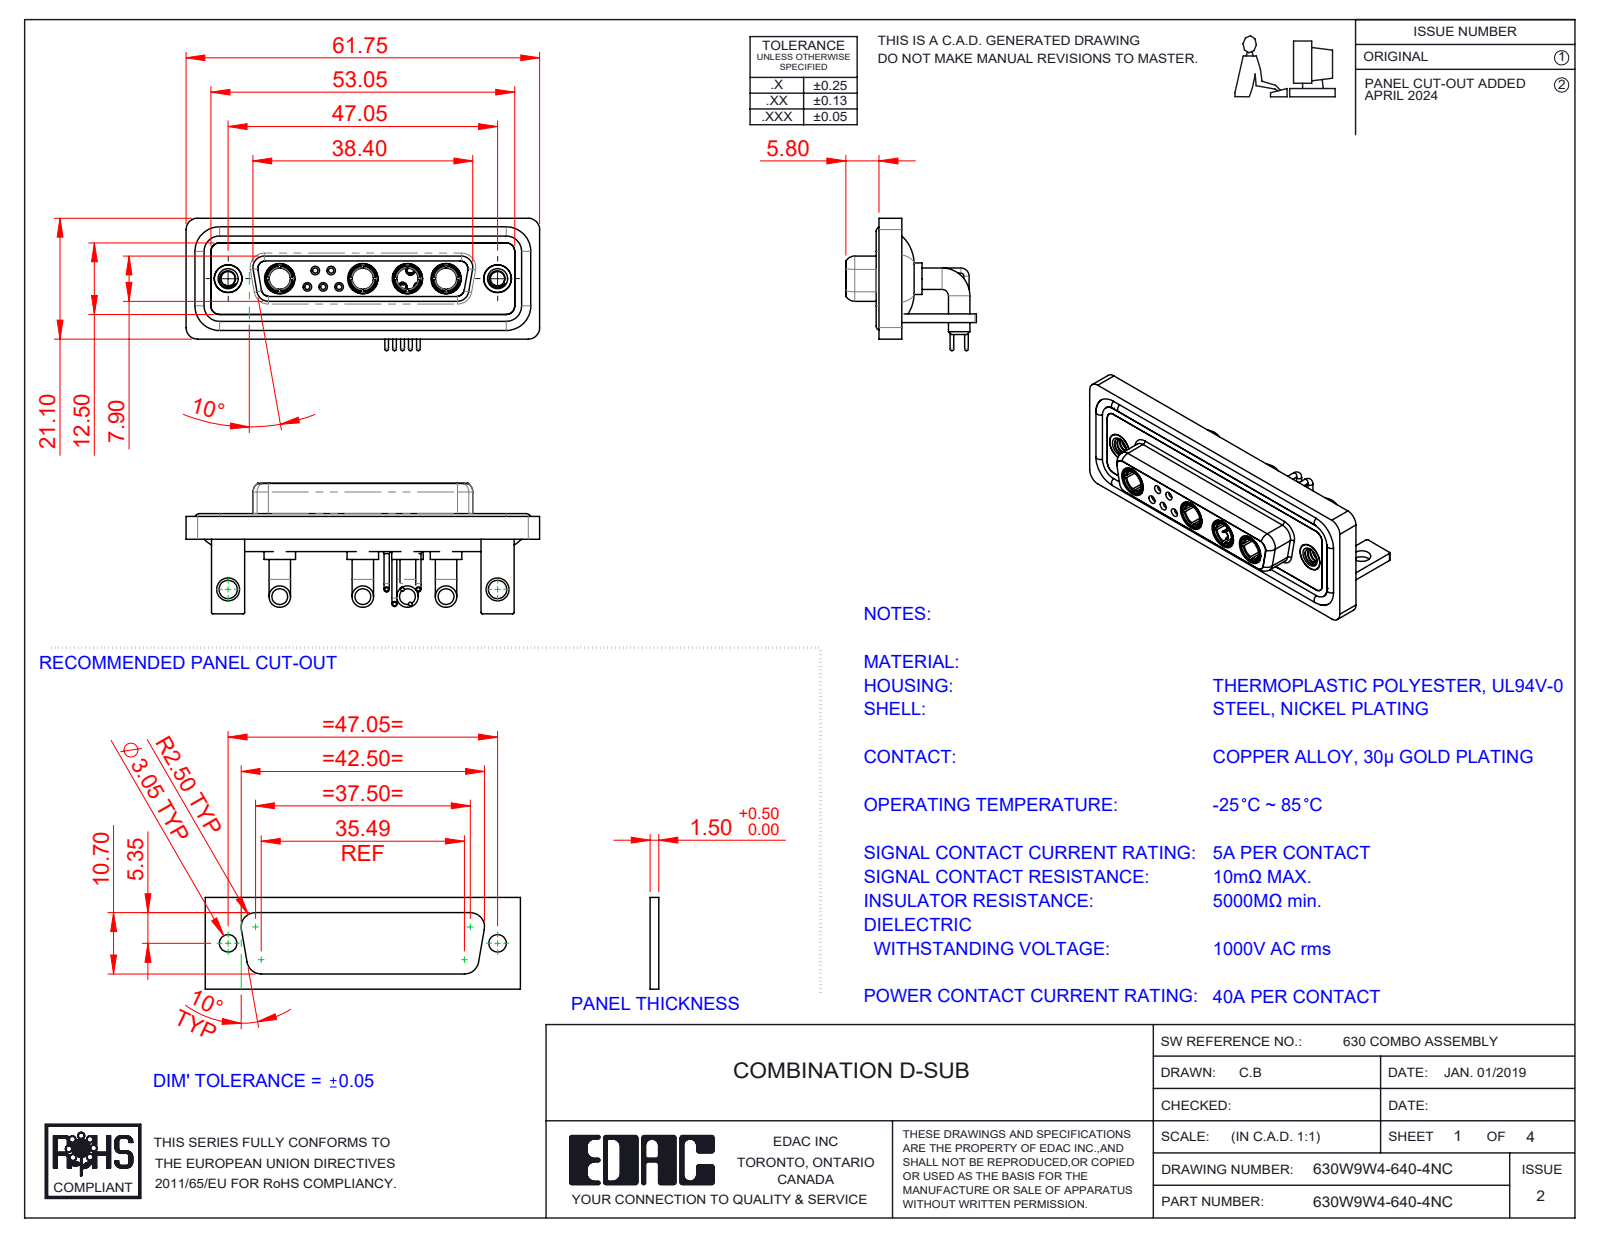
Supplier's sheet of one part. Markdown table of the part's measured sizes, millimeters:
| quantity | value |
| --- | --- |
| part name | 630Combo Housing_9W4; 630Combo Stabilizer Bracket_50 Contacts; 630Combo Contact Row 1_50 Contacts; 630Combo Waterproof Housing_25 Contacts (+6 more) |
| STEP written by | SolidWorks 2023 (CONFIG_CONTROL_DESIGN) |
| units | millimeters |
| bodies | 22 solids, 1005 faces (316 planar, 425 cylindrical, 264 other) |
| overall size | 61.75 × 23.12 × 22.8 |
| volume | 9 102 mm³ |
| surface area | 14 961 mm² |
| round holes (diameter × count) | 4.85 × 6, 0.9 × 5, 1.1 × 5, 1.5 × 5, 2 × 5, 3.7 × 4, 5.3 × 4, 1.6 × 3, 1.7 × 2, 2.5 × 2, 3.2 × 2, 4 × 2 |
| round bosses / shafts (diameter × count) | 0.9 × 10, 1.6 × 9, 3.75 × 8, 2 × 5, 1.5 × 5, 0.65 × 5, 5.5 × 4, 5.2 × 4 |
| partial cylindrical surfaces (radius × count) | 2 × 19, 1.5 × 18, 0.25 × 16, 1.35 × 8, 1.6 × 8, 0.5 × 5, 0.6 × 4, 0.65 × 4 |
| main face-to-face distances | 0.4, 1.8, 2.9, 3.7, 1.5, 4.1, 1.1, 1.4, 1.6, 2.5 |
| hole center spacings | 3.16, 2.77, 5.04, 13.85, 11.08, 12.79, 15.5, 5.54 |
